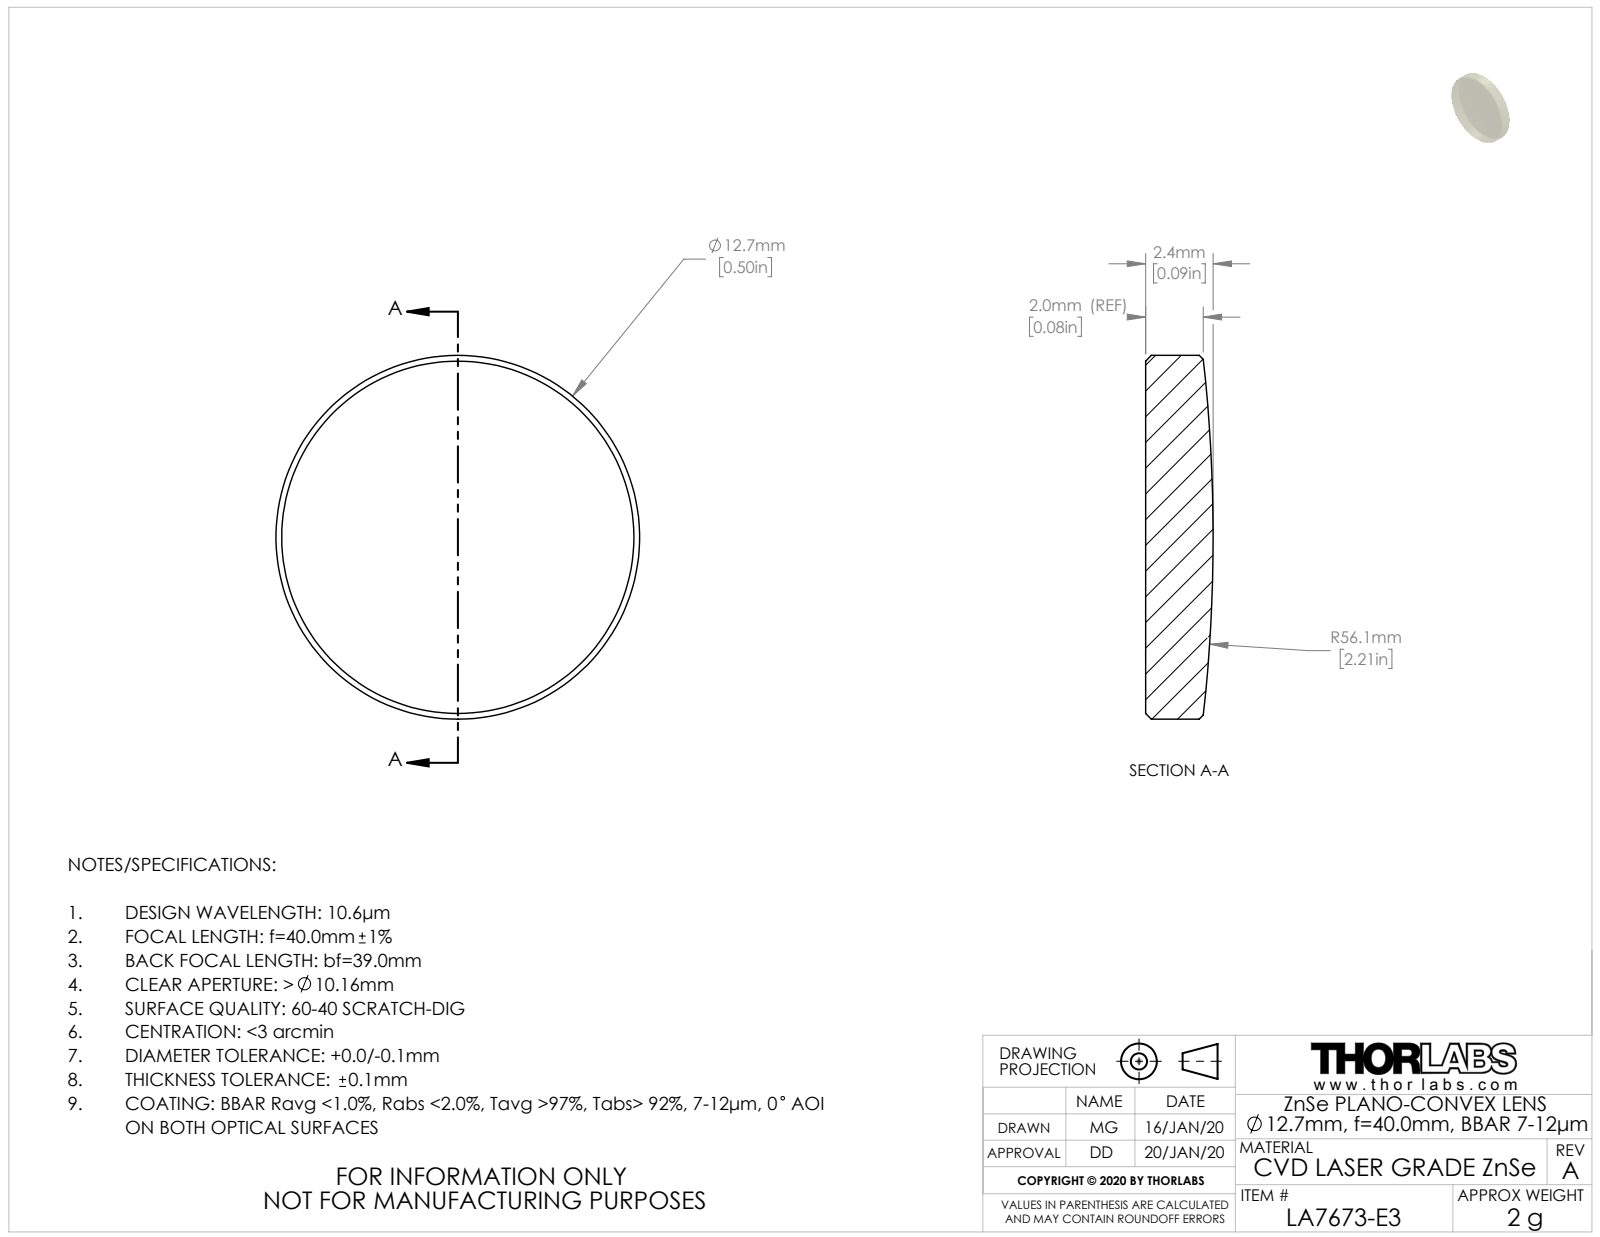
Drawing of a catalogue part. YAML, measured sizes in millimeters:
part_name: "TTN206022-E0W"
step_written_by: "SolidWorks 2018 (CONFIG_CONTROL_DESIGN)"
units: millimeters
bodies: {solids: 1, faces: 9, planar: 1, cylindrical: 2, other: 6}
overall_size: [12.7, 12.7, 2.36]
volume: 275
surface_area: 326
round_bosses_or_shafts:
  - {diameter: 12.7, count: 1}
